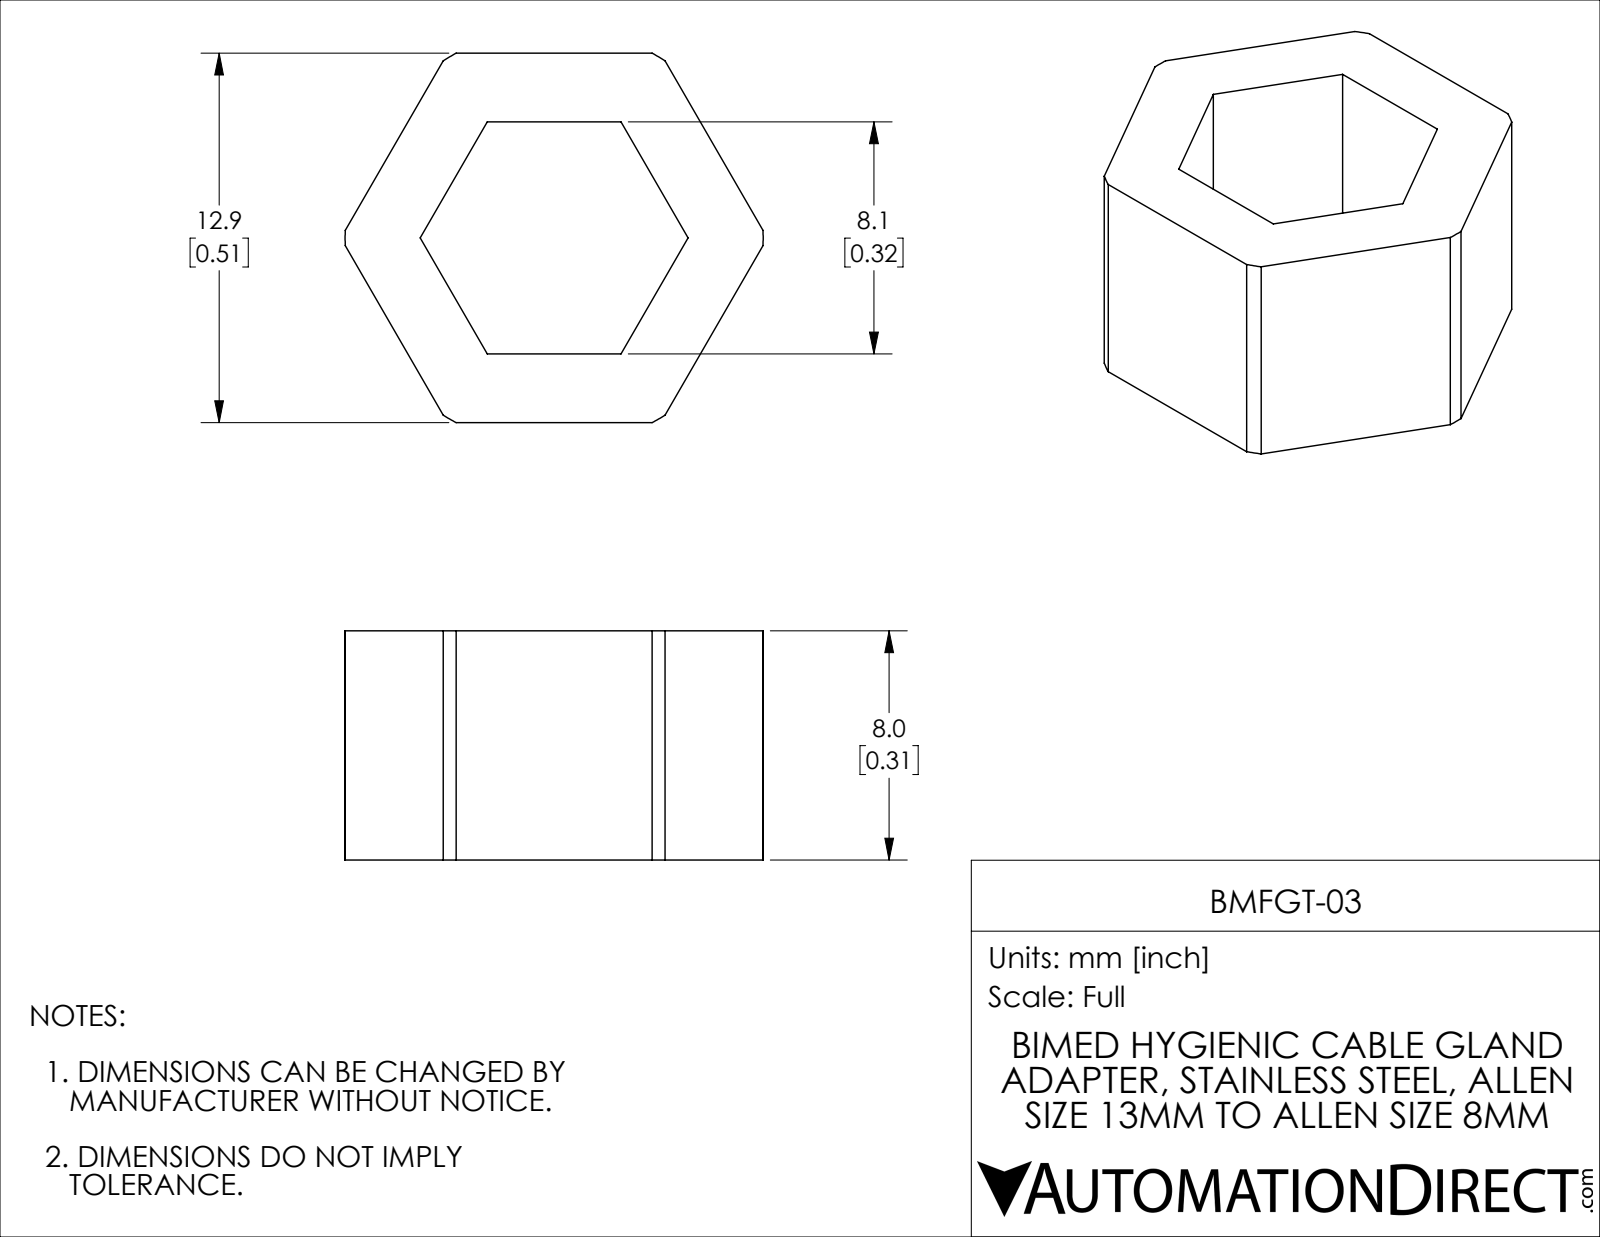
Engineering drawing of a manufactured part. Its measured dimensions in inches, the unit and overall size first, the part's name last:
Units: inches
Overall size (bounding box): 0.575 × 0.508 × 0.315
Partial cylindrical surfaces — rounded edges, fillets, slot ends (radius × count): R0.287 ×1
Main face-to-face distances: 0.094, 0.413, 0.508, 0.319, 0.315
Volume: 0.043 in³ · Surface area: 1.17 in²
Bodies: 1 solid, 20 faces (14 planar, 6 cylindrical, 0 other)
Part name (STEP PRODUCT): BMFGT-03
STEP written by: SolidWorks 2021 (CONFIG_CONTROL_DESIGN)
